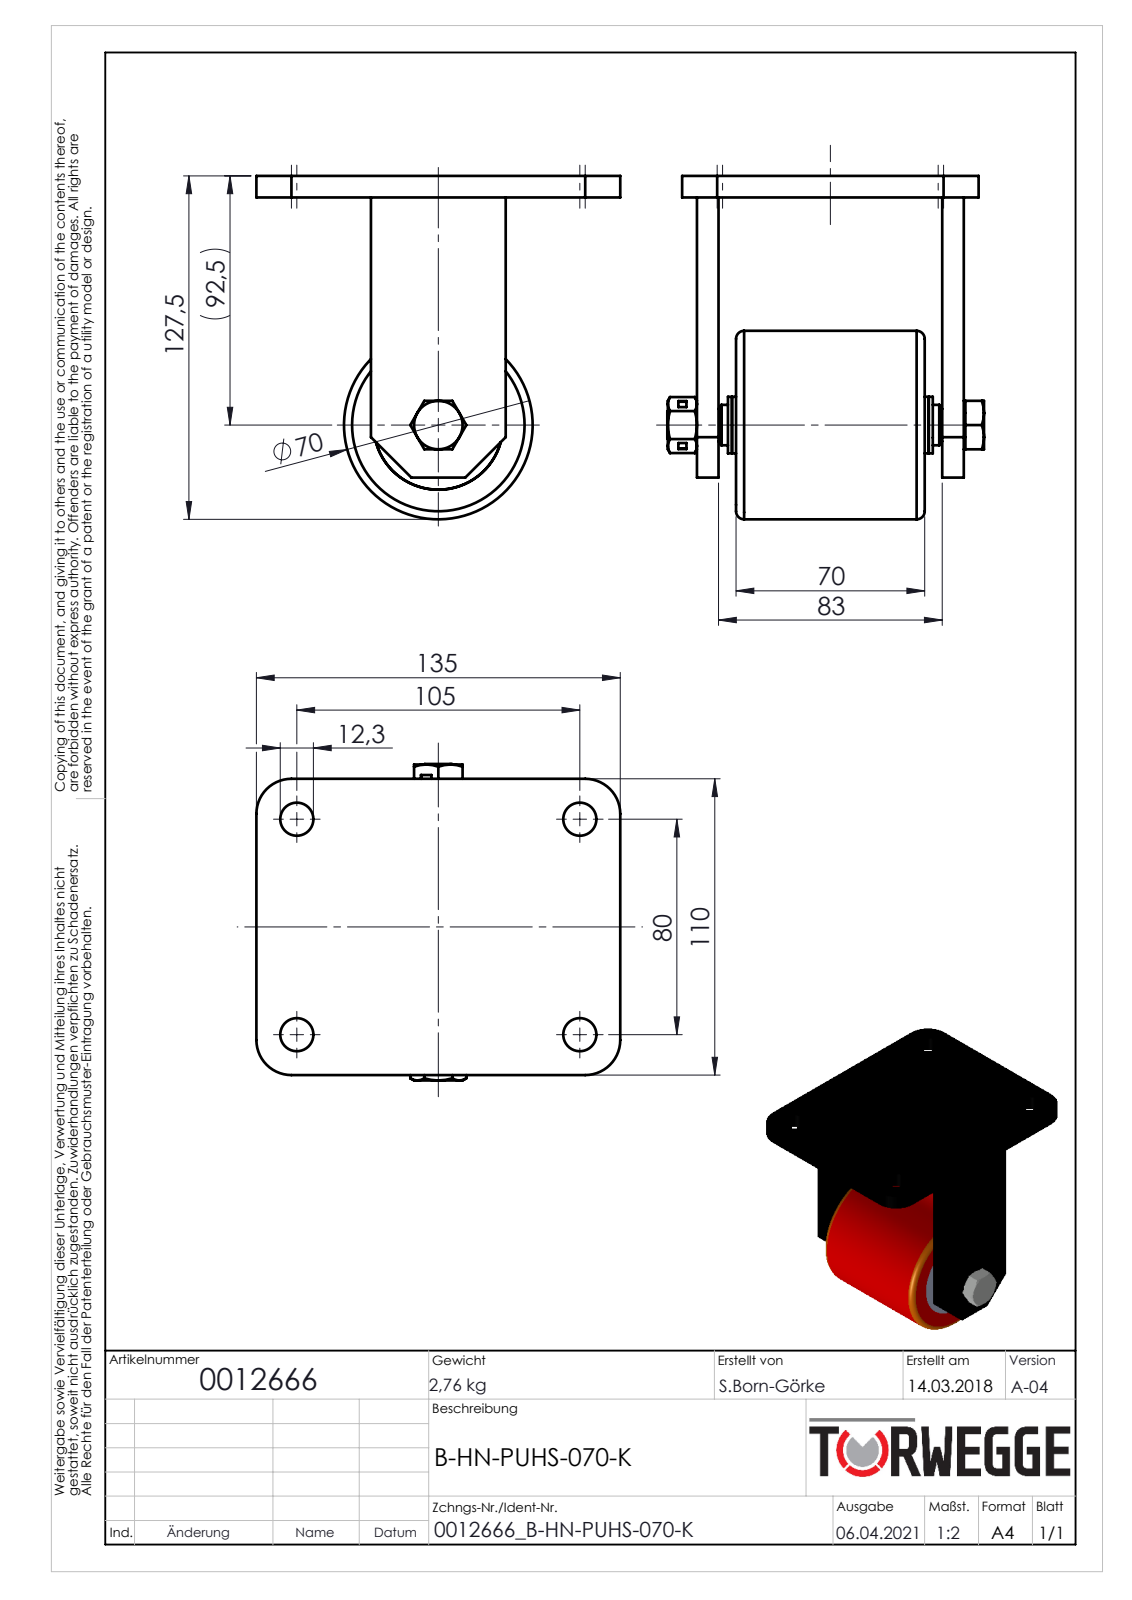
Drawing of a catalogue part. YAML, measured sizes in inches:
part_name: "0012666"
step_written_by: "SolidWorks 2020 (AUTOMOTIVE_DESIGN)"
units: inches
bodies: {solids: 22, faces: 266, planar: 92, cylindrical: 96, other: 78}
overall_size: [5.315, 5.02, 4.626]
volume: 26.72
surface_area: 213.1
round_holes:
  - {diameter: 0.484, count: 4}
  - {diameter: 0.402, count: 1}
  - {diameter: 0.472, count: 1}
  - {diameter: 0.488, count: 1}
  - {diameter: 0.591, count: 1}
  - {diameter: 1.142, count: 1}
  - {diameter: 1.24, count: 1}
  - {diameter: 1.378, count: 1}
  - {diameter: 1.89, count: 1}
round_bosses_or_shafts:
  - {diameter: 2.756, count: 1}
  - {diameter: 0.827, count: 1}
  - {diameter: 0.709, count: 1}
partial_cylinders:
  - {radius: 0.512, count: 4}
face_to_face_distances: [0.315, 3.583, 3.012, 0.571, 3.327, 0.256, 3.898, 3.268, 2.756, 2.323]
hole_center_spacings: [3.15, 4.134, 5.197]
